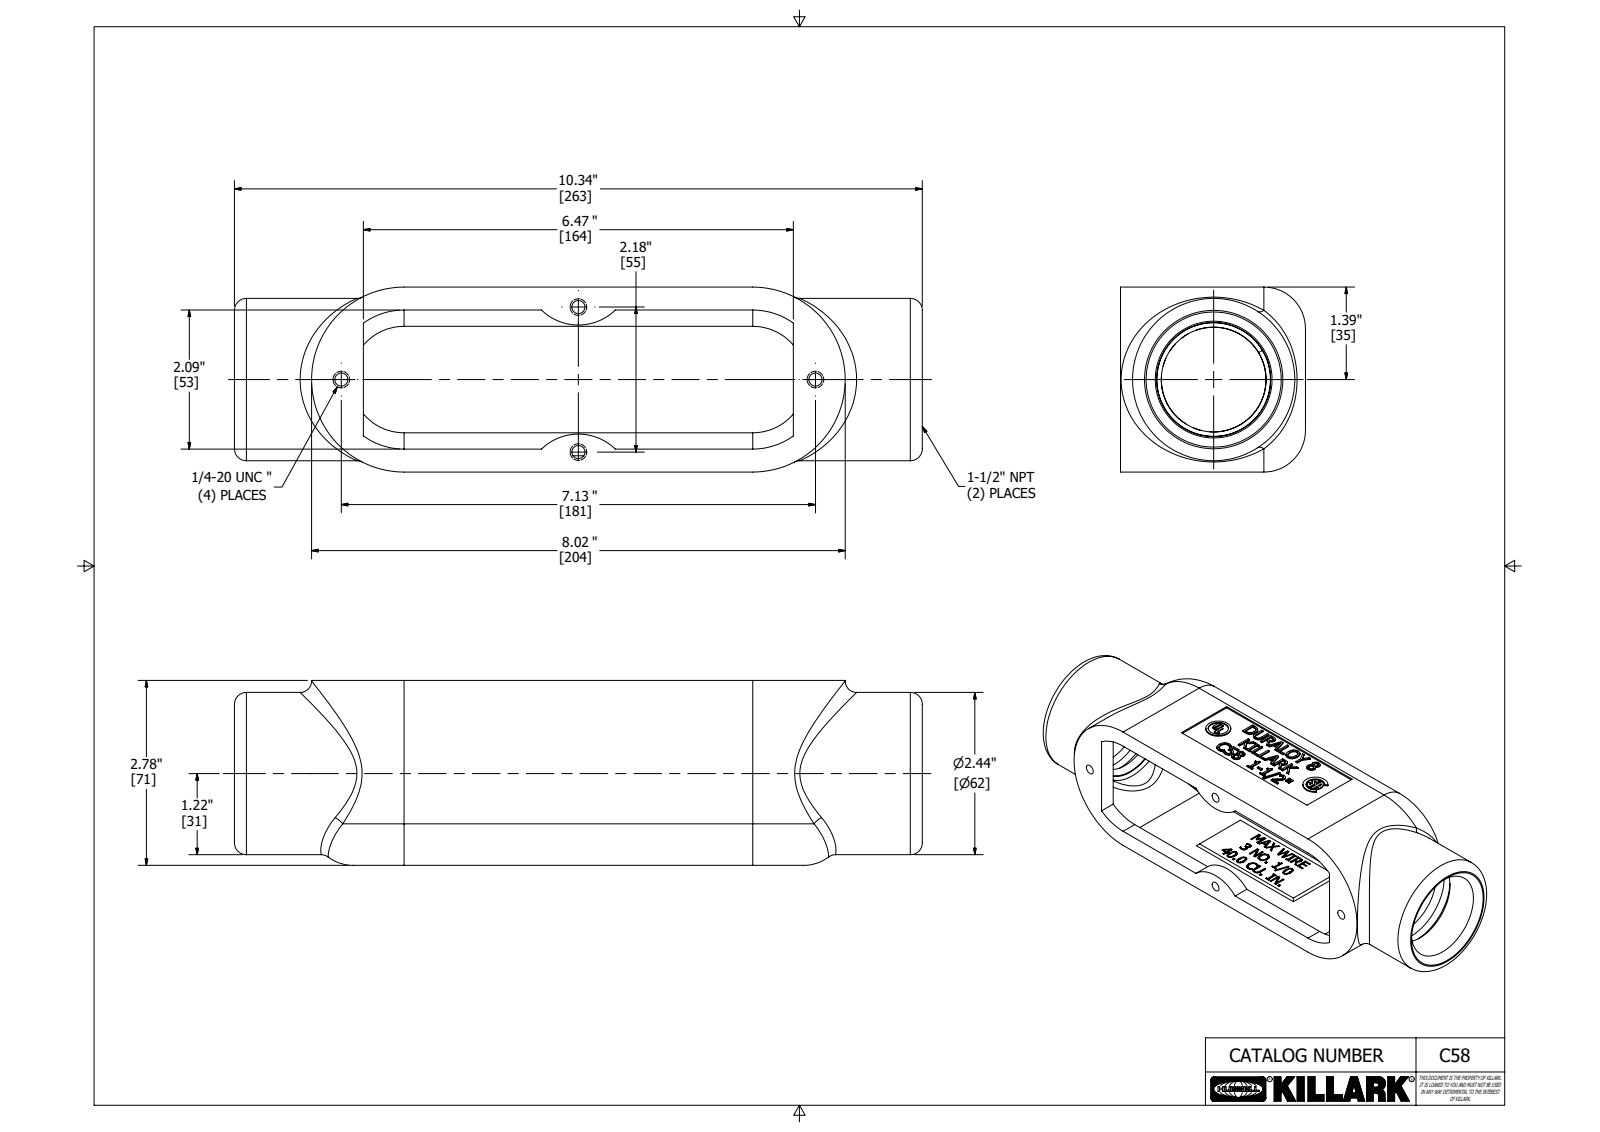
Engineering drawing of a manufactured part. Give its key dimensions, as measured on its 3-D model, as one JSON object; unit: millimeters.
{"part_name": "21710-2", "step_written_by": "Autodesk Inventor 2018 (AUTOMOTIVE_DESIGN)", "units": "millimeters", "bodies": {"solids": 1, "faces": 777, "planar": 478, "cylindrical": 40, "other": 259}, "overall_size": [262.7, 70.6, 70.6], "volume_mm3": 309900, "surface_area_mm2": 110200, "round_holes": [[5, 4], [10.3, 1], [48.4, 1]], "round_bosses_or_shafts": [[62, 1], [12.7, 1]], "partial_cylinders_radius": [[9.9, 2], [15.9, 2], [20.2, 2], [26.5, 2], [30.2, 2], [35.3, 2], [0.4, 1], [1.6, 1]], "face_to_face_distances": [65.5, 5.1, 70.6, 60.5, 69.9, 64.8, 4.3, 0.8, 8.4, 62.2], "hole_center_spacings": [94.7, 55.4, 181.1]}
